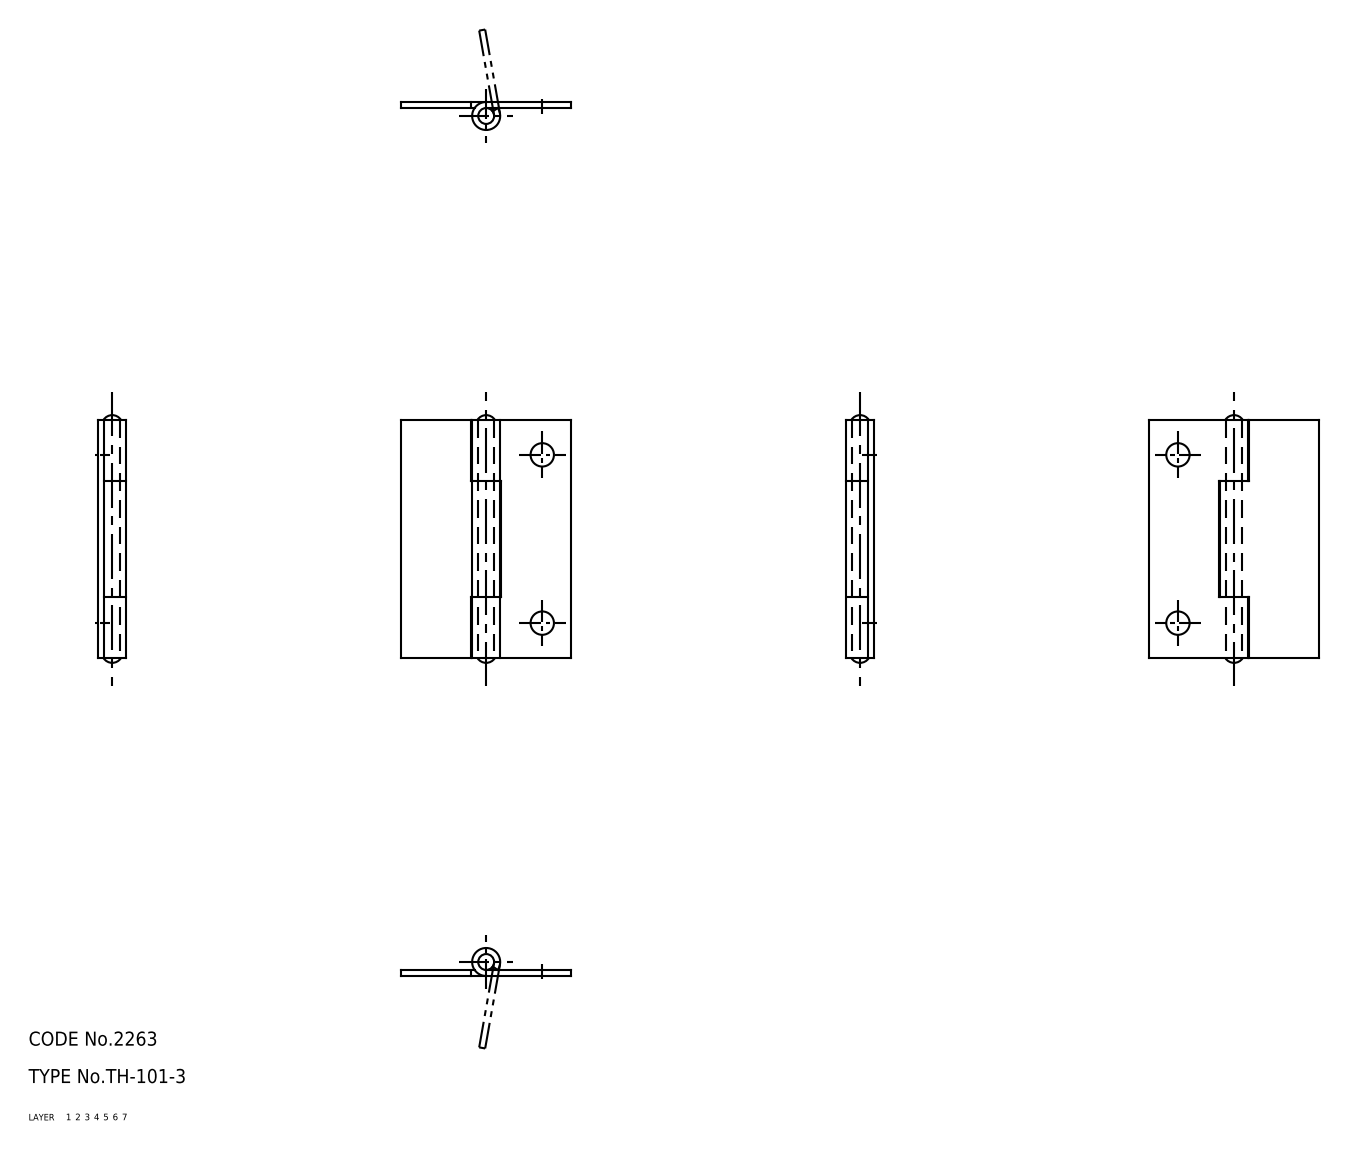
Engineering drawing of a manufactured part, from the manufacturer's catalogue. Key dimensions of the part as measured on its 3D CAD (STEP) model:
Part name (STEP PRODUCT): 67110973; 67110986; 67110999
STEP written by: CADfix (AUTOMOTIVE_DESIGN)
Units: millimetres
Bodies: 3 solids, 36 faces (0 planar, 0 cylindrical, 36 other)
Overall size (bounding box): 53 × 36.5 × 6
Volume: 3 454 mm³ · Surface area: 5 665 mm²
